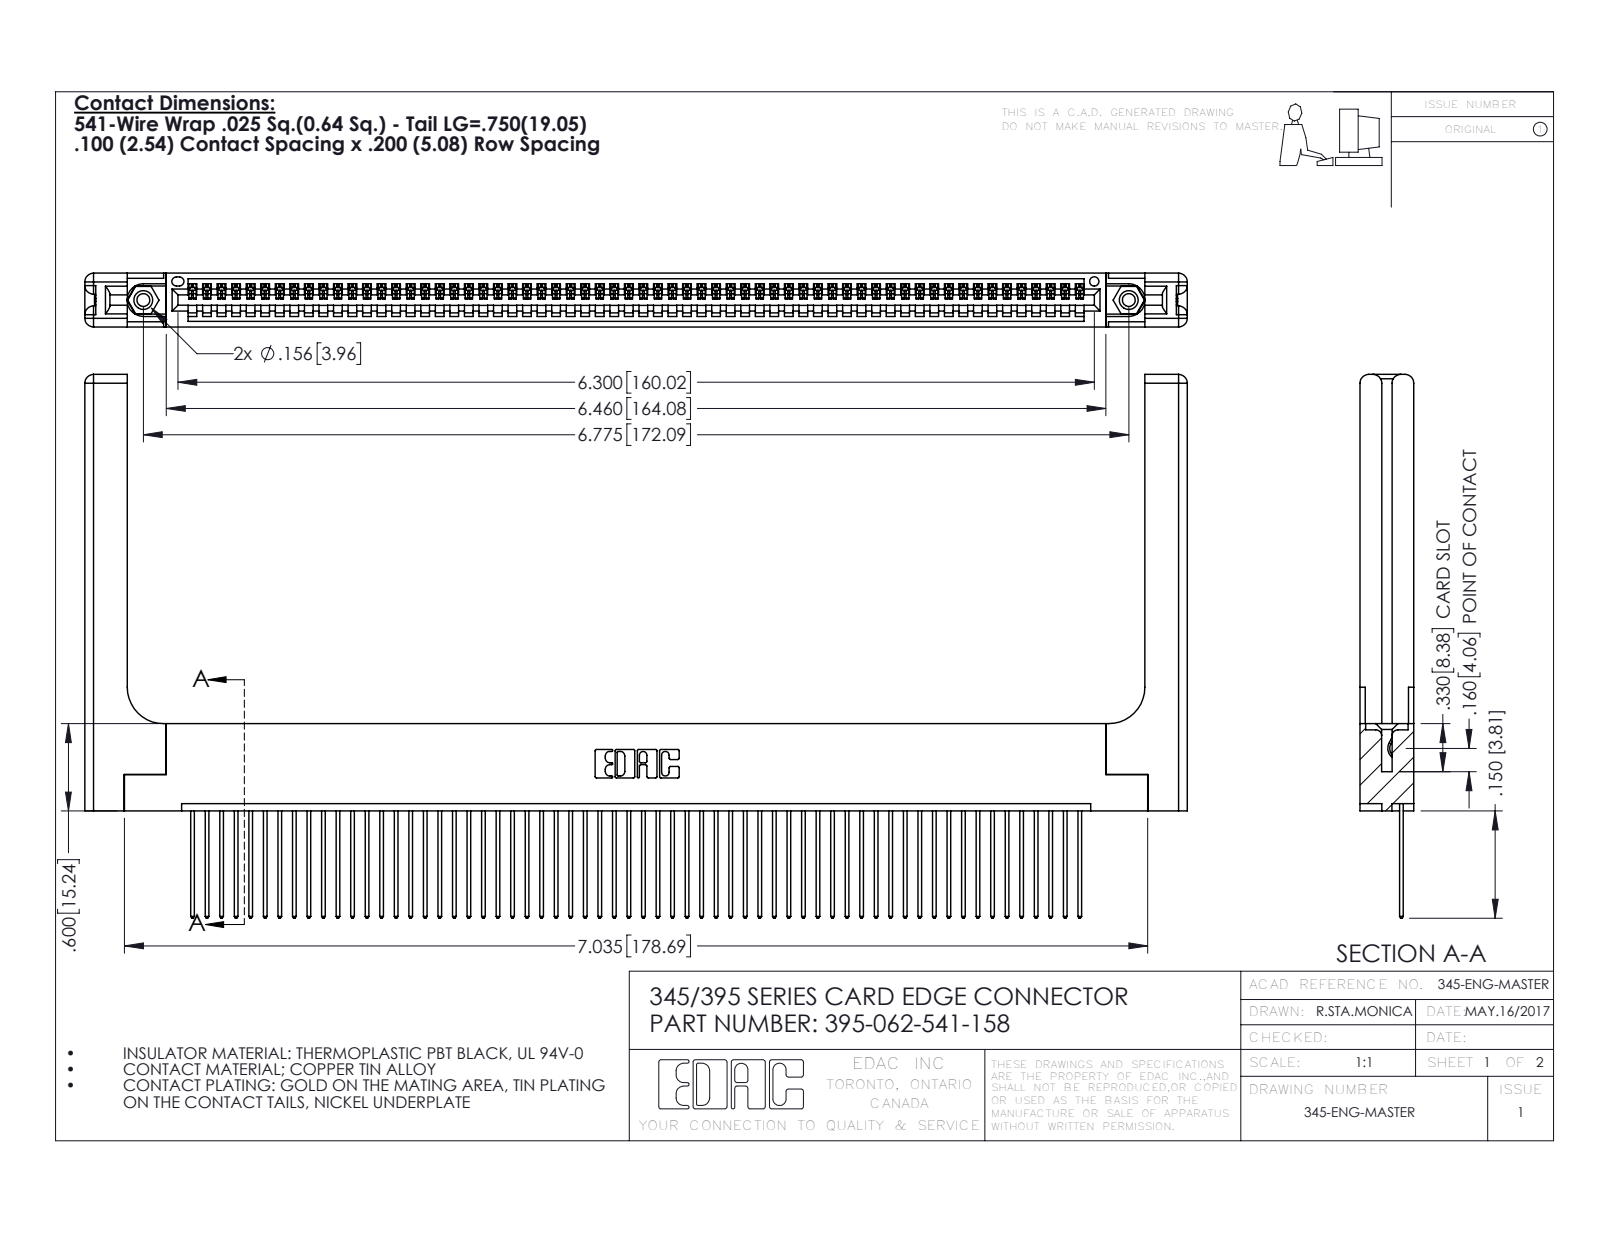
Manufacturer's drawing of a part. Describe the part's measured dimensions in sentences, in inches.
The part is named "345-292-001_345-293-141; 345-220-058_345-220-058; 395-062-541-158; 345-250-001_345-250-001-102 (+1 more)". Its 3-D file was written by "SolidWorks 2016 (CONFIG_CONTROL_DESIGN)". It is 67 solids with 3978 faces: 2708 planar, 1210 cylindrical and 60 other. Overall it measures 7.579 by 3.737 by 0.37 inches. Its volume is 1.657 cubic inches and its surface area 48.93 square inches. Round holes: 2 of diameter 0.089, 2 of diameter 0.125, 2 of diameter 0.156, 1 of diameter 0.064. Round bosses or shafts: 2 of diameter 0.155. Partial cylindrical surfaces (rounded edges, fillets, slot ends): 124 of radius 0.006, 124 of radius 0.01, 22 of radius 0.01, 16 of radius 0.06, 6 of radius 0.007, 6 of radius 0.031, 3 of radius 0.026, 2 of radius 0.03. The main face-to-face distances are 0.072, 0.298, 0.37, 0.098, 0.272, 0.025, 0.2, 0.225, 0.15, 0.148. The hole center spacings are 0.27, 6.539, 6.775.
